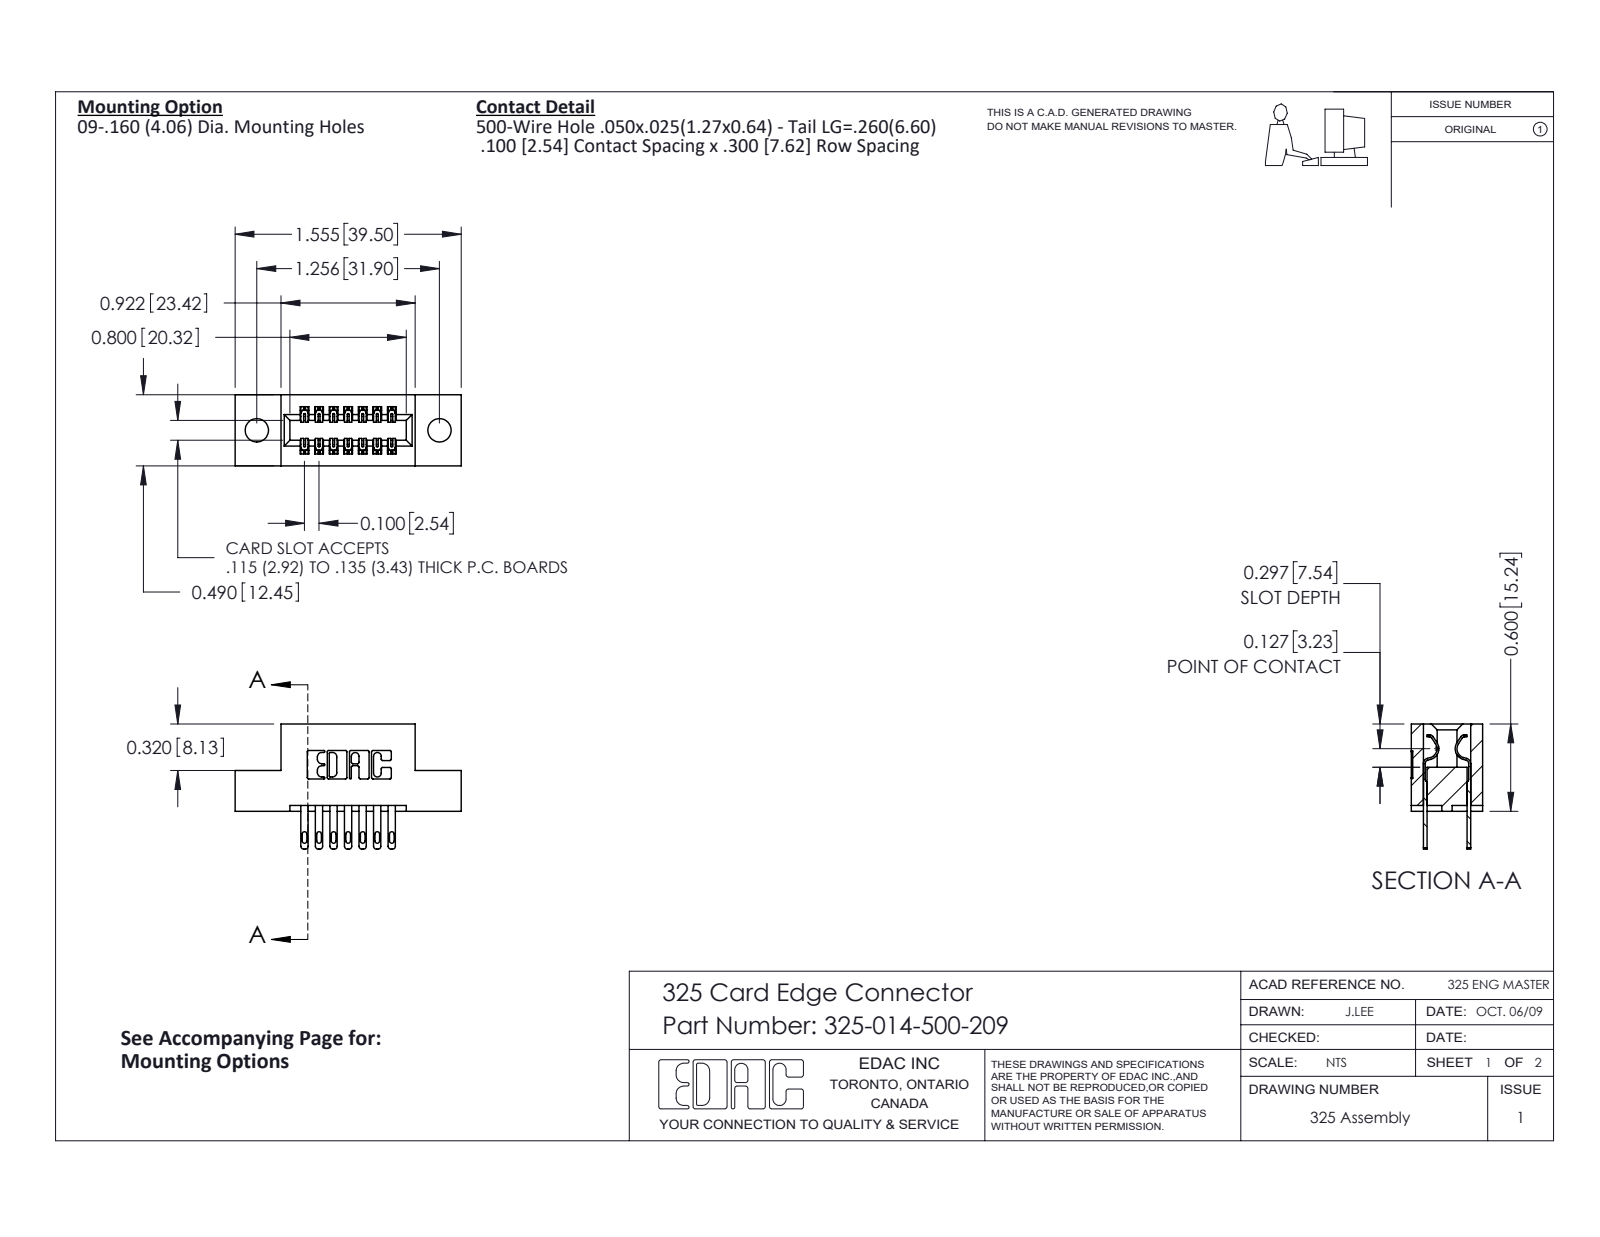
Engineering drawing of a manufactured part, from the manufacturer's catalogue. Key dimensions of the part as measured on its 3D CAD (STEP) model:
Part name (STEP PRODUCT): 325 Part_.160 TH; 325-292-001_325-293-100; 325-014-500-209
STEP written by: SolidWorks 2016 (CONFIG_CONTROL_DESIGN)
Units: inches
Bodies: 15 solids, 786 faces (490 planar, 296 cylindrical, 0 other)
Overall size (bounding box): 1.555 × 0.86 × 0.49
Volume: 0.281 in³ · Surface area: 7.441 in²
Round holes (diameter × count): ⌀0.16 ×2
Partial cylindrical surfaces — rounded edges, fillets, slot ends (radius × count): R0.01 ×22, R0.006 ×21, R0.016 ×14, R0.02 ×14, R0.007 ×6, R0.031 ×6, R0.026 ×3, R0.014 ×2
Main face-to-face distances: 0.3, 0.083, 0.407, 0.1, 0.04, 0.2, 0.49, 0.107, 0.383, 0.025
Hole centre spacings: 1.256
